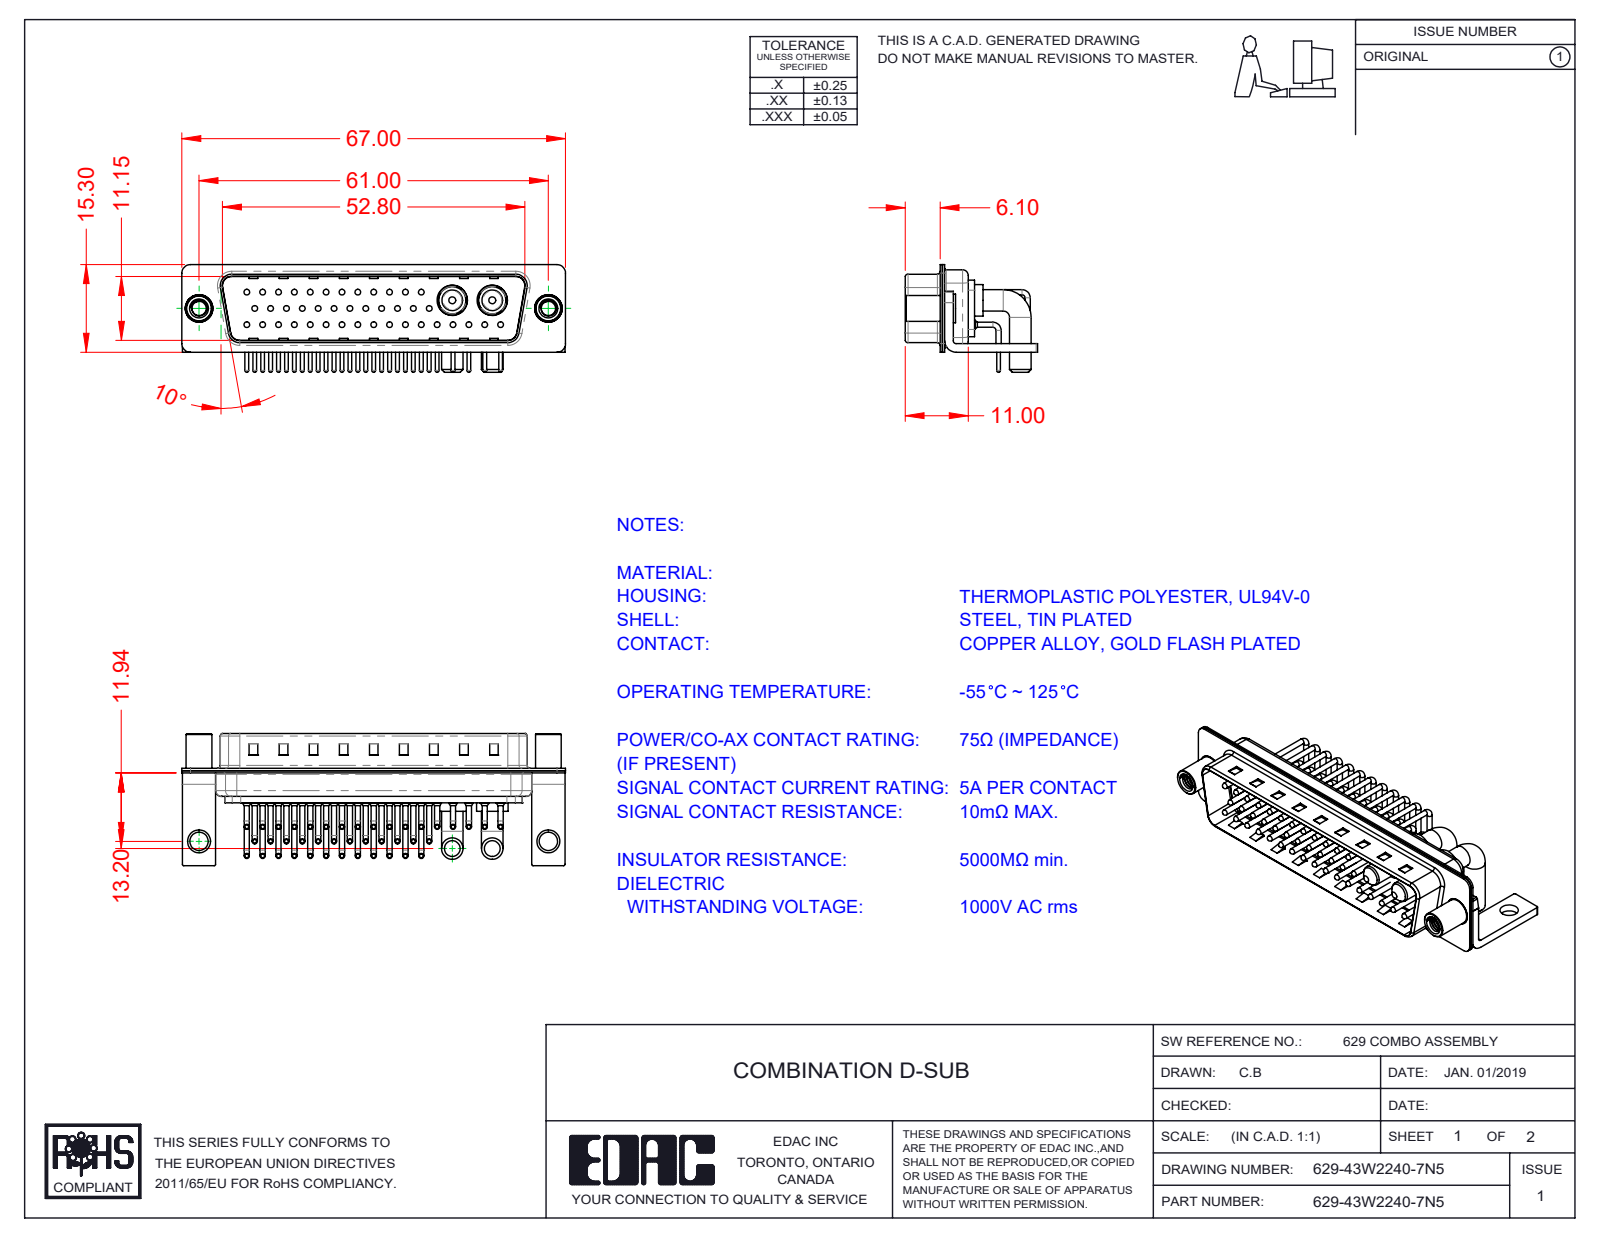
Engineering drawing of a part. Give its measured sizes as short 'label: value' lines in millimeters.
name: 629Combo Housing_43W2; Power Pin_40A RA 50; 629-43W2240-7N5; 629Combo Contact Row 2_50 Contacts (+6 more)
written by: SolidWorks 2020 (CONFIG_CONTROL_DESIGN)
unit: mm
bodies: 52 solids, 5106 faces (2869 planar, 1731 cylindrical, 506 other)
size: 67 × 23.1 × 18.8
volume: 5 837 mm³; area: 13 730 mm²
holes: 41× ⌀0.75, 41× ⌀1.6, 41× ⌀2, 2× ⌀2.5, 2× ⌀3.2, 2× ⌀4, 2× ⌀4.8, 2× ⌀4.85, 2× ⌀5.3
bosses: 82× ⌀0.9, 41× ⌀1.5, 41× ⌀1, 41× ⌀0.65, 4× ⌀3.75, 2× ⌀5.5, 2× ⌀5.2, 2× ⌀5
rounds: 41× R1.01, 16× R0.25, 16× R1.5, 13× R2, 9× R0.5, 8× R1.6, 4× R0.6, 4× R0.65
face distances: 0.4, 1.5, 11.55, 5.6, 5.2, 0.8, 1.9, 4.1, 6, 0.78
hole spacings: 2.77, 5.54, 3.16, 8.31, 11.08, 13.85, 16.62, 19.39
